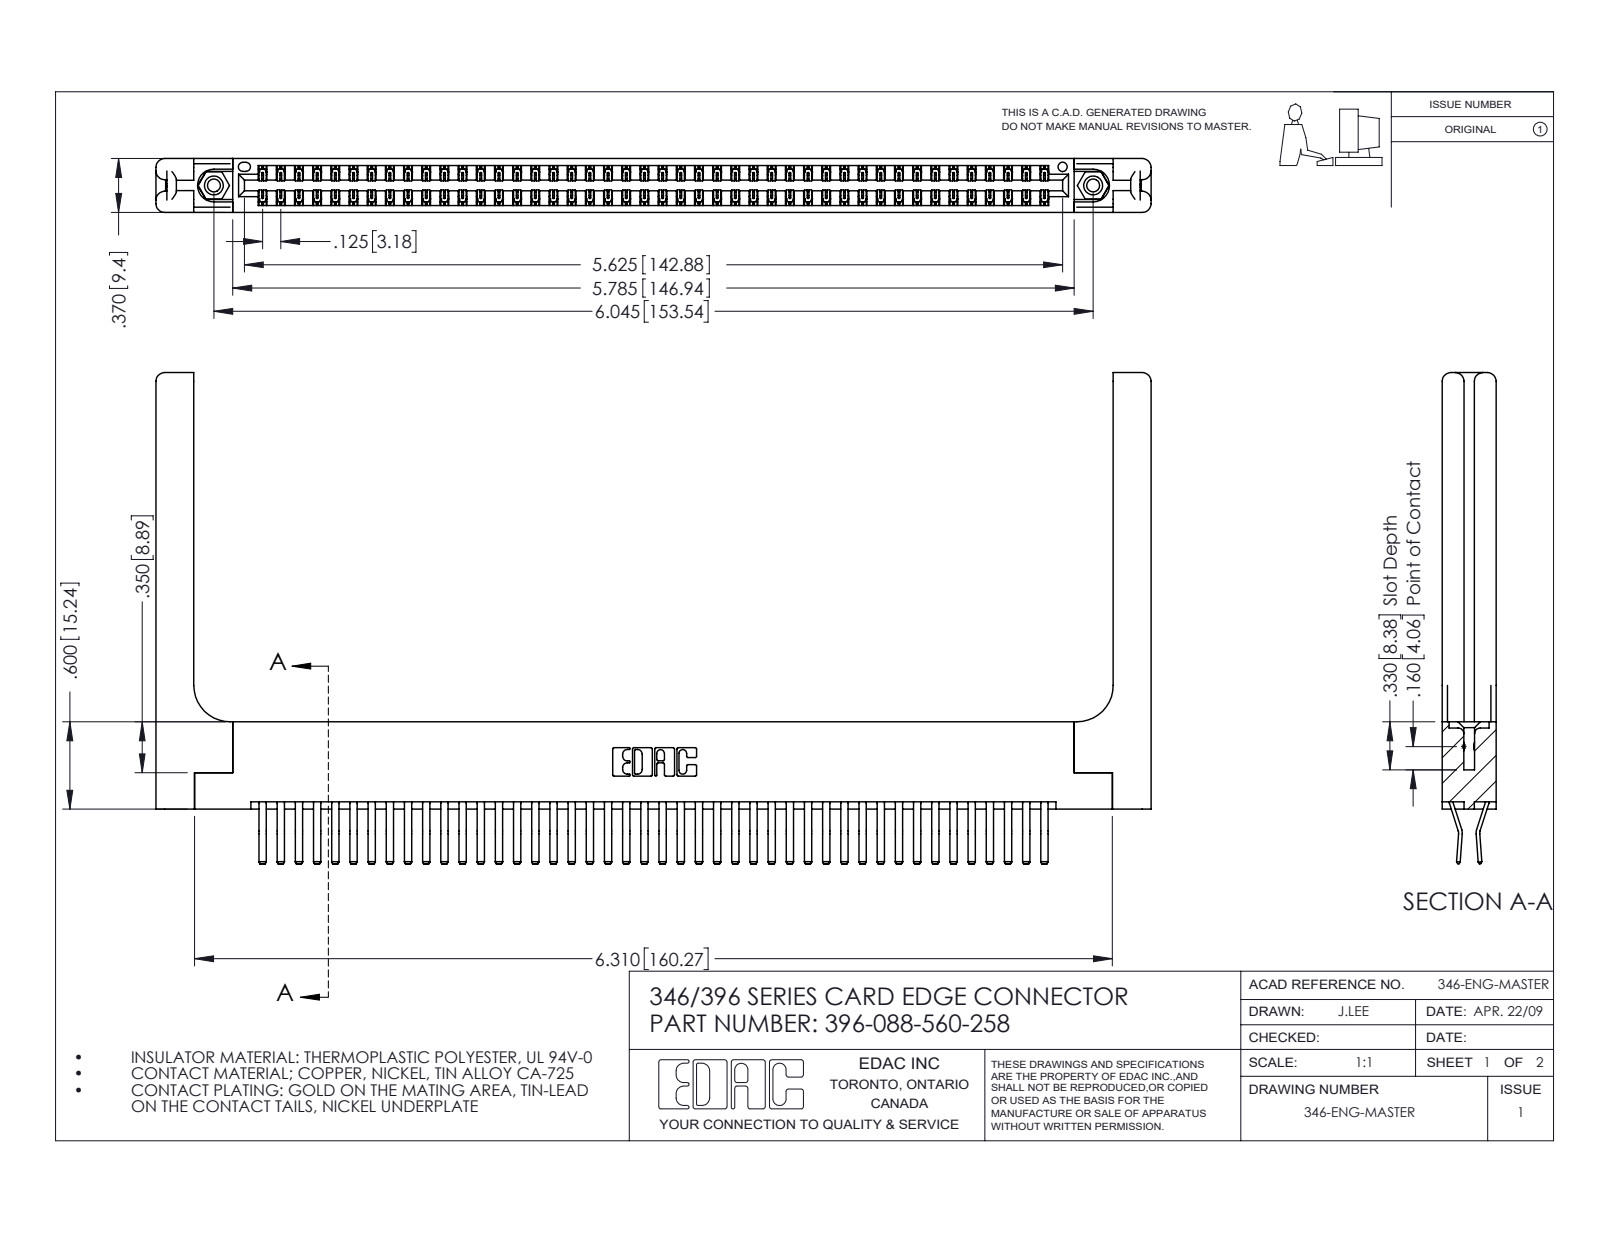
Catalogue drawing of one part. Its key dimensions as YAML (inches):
part_name: "396-088-560-258; 346-220-058_345-220-058; 346 Part_Flush Mounting Lugs - 0.156 Dia-TH; 345-250-001_345-250-001-102 (+1 more)"
step_written_by: "SolidWorks 2016 (CONFIG_CONTROL_DESIGN)"
units: inches
bodies: {solids: 93, faces: 5130, planar: 3304, cylindrical: 1766, other: 60}
overall_size: [6.841, 3.375, 0.37]
volume: 1.527
surface_area: 47.5
round_holes:
  - {diameter: 0.089, count: 2}
  - {diameter: 0.125, count: 2}
  - {diameter: 0.156, count: 2}
  - {diameter: 0.064, count: 1}
round_bosses_or_shafts:
  - {diameter: 0.155, count: 2}
partial_cylinders:
  - {radius: 0.006, count: 132}
  - {radius: 0.01, count: 22}
  - {radius: 0.06, count: 16}
  - {radius: 0.007, count: 6}
  - {radius: 0.031, count: 6}
  - {radius: 0.026, count: 3}
  - {radius: 0.01, count: 2}
  - {radius: 0.014, count: 2}
face_to_face_distances: [0.37, 0.048, 0.322, 0.072, 0.025, 0.148, 0.15, 0.25, 0.298, 0.275]
hole_center_spacings: [0.246, 5.836, 6.045]
